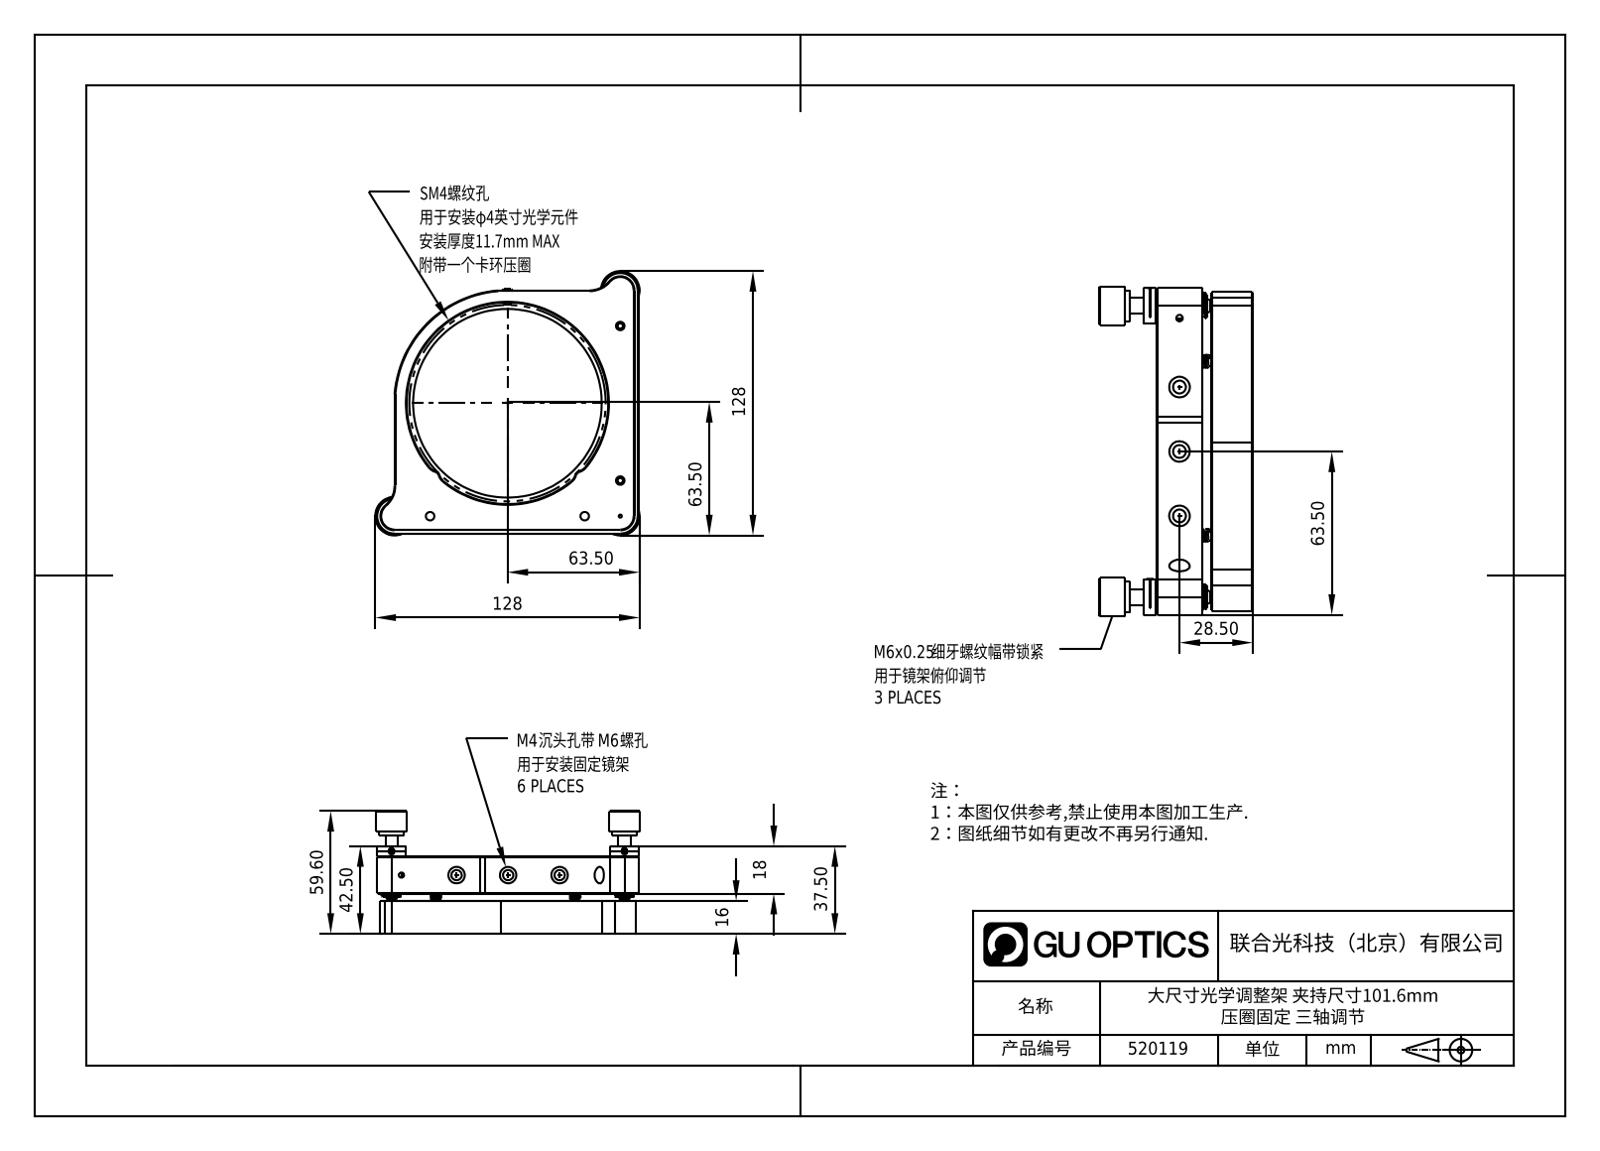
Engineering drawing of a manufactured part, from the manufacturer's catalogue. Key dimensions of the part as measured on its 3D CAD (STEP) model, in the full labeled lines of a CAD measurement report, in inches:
Part name (STEP PRODUCT): 520119
STEP written by: SolidWorks 2020 (CONFIG_CONTROL_DESIGN)
Units: inches
Bodies: 0 solids, 318 faces (155 planar, 82 cylindrical, 81 other)
Overall size (bounding box): 5.039 × 5.039 × 2.35
Round holes (diameter × count): ⌀0.197 ×6, ⌀0.315 ×6, ⌀0.256 ×4, ⌀0.098 ×3, ⌀0.374 ×3, ⌀0.157 ×1, ⌀3.811 ×1
Round bosses / shafts (diameter × count): ⌀0.13 ×4, ⌀0.079 ×4, ⌀0.591 ×3, ⌀0.551 ×3, ⌀0.236 ×3, ⌀0.315 ×2, ⌀0.047 ×2, ⌀4.054 ×1
Partial cylindrical surfaces — rounded edges, fillets, slot ends (radius × count): R0.041 ×8, R0.197 ×7, R0.217 ×3, R0.315 ×2, R0.394 ×2, R0.008 ×1, R2.008 ×1, R2.229 ×1
Main face-to-face distances: 0.63, 0.846, 1.476, 0.768, 0.709, 0.138, 0.059, 0.039, 4.724, 4.665
Hole centre spacings: 0.984, 1.053, 2.037, 3.022, 3.146, 0.846, 0.945, 1.969
